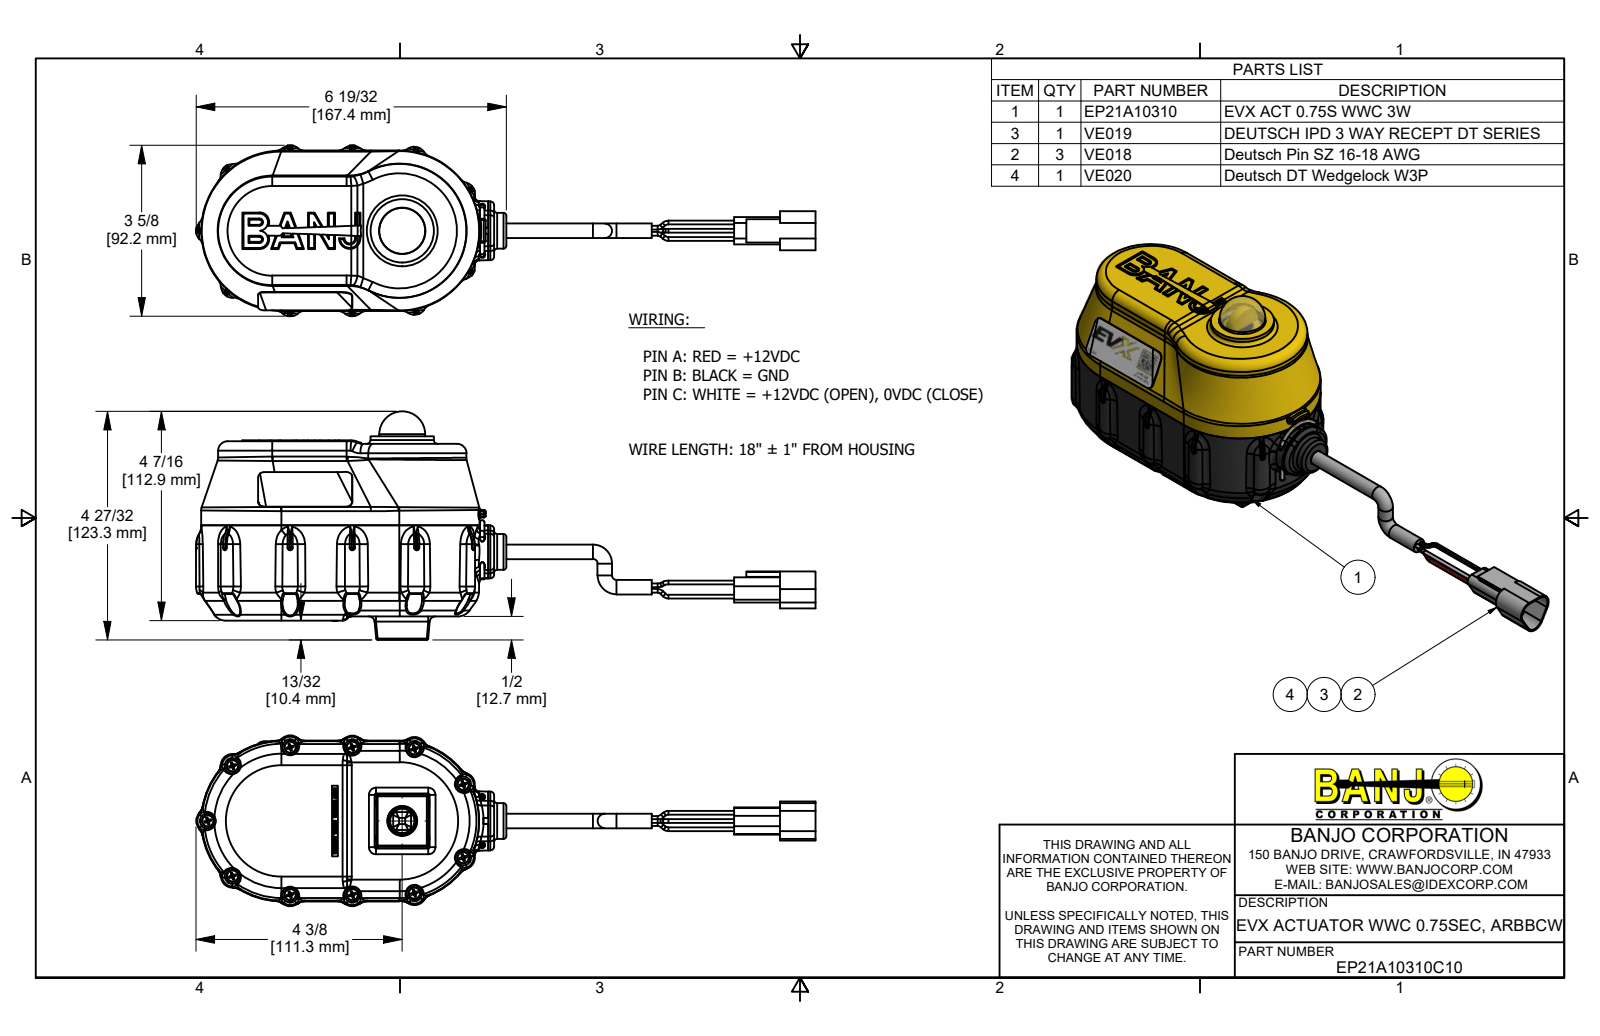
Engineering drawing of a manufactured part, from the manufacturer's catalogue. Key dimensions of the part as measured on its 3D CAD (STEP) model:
Part name (STEP PRODUCT): EP21A10310C10; EP21A10310; EP10310; IRF4905 (+8 more)
STEP written by: Autodesk Inventor 2019 (AUTOMOTIVE_DESIGN)
Units: inches
Bodies: 78 solids, 10156 faces (2663 planar, 2976 cylindrical, 4517 other)
Overall size (bounding box): 13.165 × 4.853 × 3.63
Volume: 31.54 in³ · Surface area: 413.7 in²
Round holes (diameter × count): ⌀0.095 ×11, ⌀0.15 ×11, ⌀0.08 ×7, ⌀0.107 ×4, ⌀0.126 ×4, ⌀0.136 ×4, ⌀0.148 ×4, ⌀0.15 ×4, ⌀0.17 ×4, ⌀0.02 ×3, ⌀0.06 ×3, ⌀0.061 ×3
Round bosses / shafts (diameter × count): ⌀0.25 ×17, ⌀0.08 ×15, ⌀0.14 ×11, ⌀0.108 ×11, ⌀0.085 ×11, ⌀0.058 ×6, ⌀0.27 ×4, ⌀0.219 ×4
Partial cylindrical surfaces — rounded edges, fillets, slot ends (radius × count): R0.013 ×180, R0.04 ×145, R0.01 ×84, R0.02 ×76, R0.005 ×54, R0.08 ×28, R0.03 ×26, R0.014 ×22
Main face-to-face distances: 0.1, 2.565, 0.211, 0.06, 0.151, 1.896, 1.685, 1.836, 2.465, 0.78
Hole centre spacings: 1.283, 0.33, 1.513, 2.69, 2.849, 3.789, 0.487, 0.668
